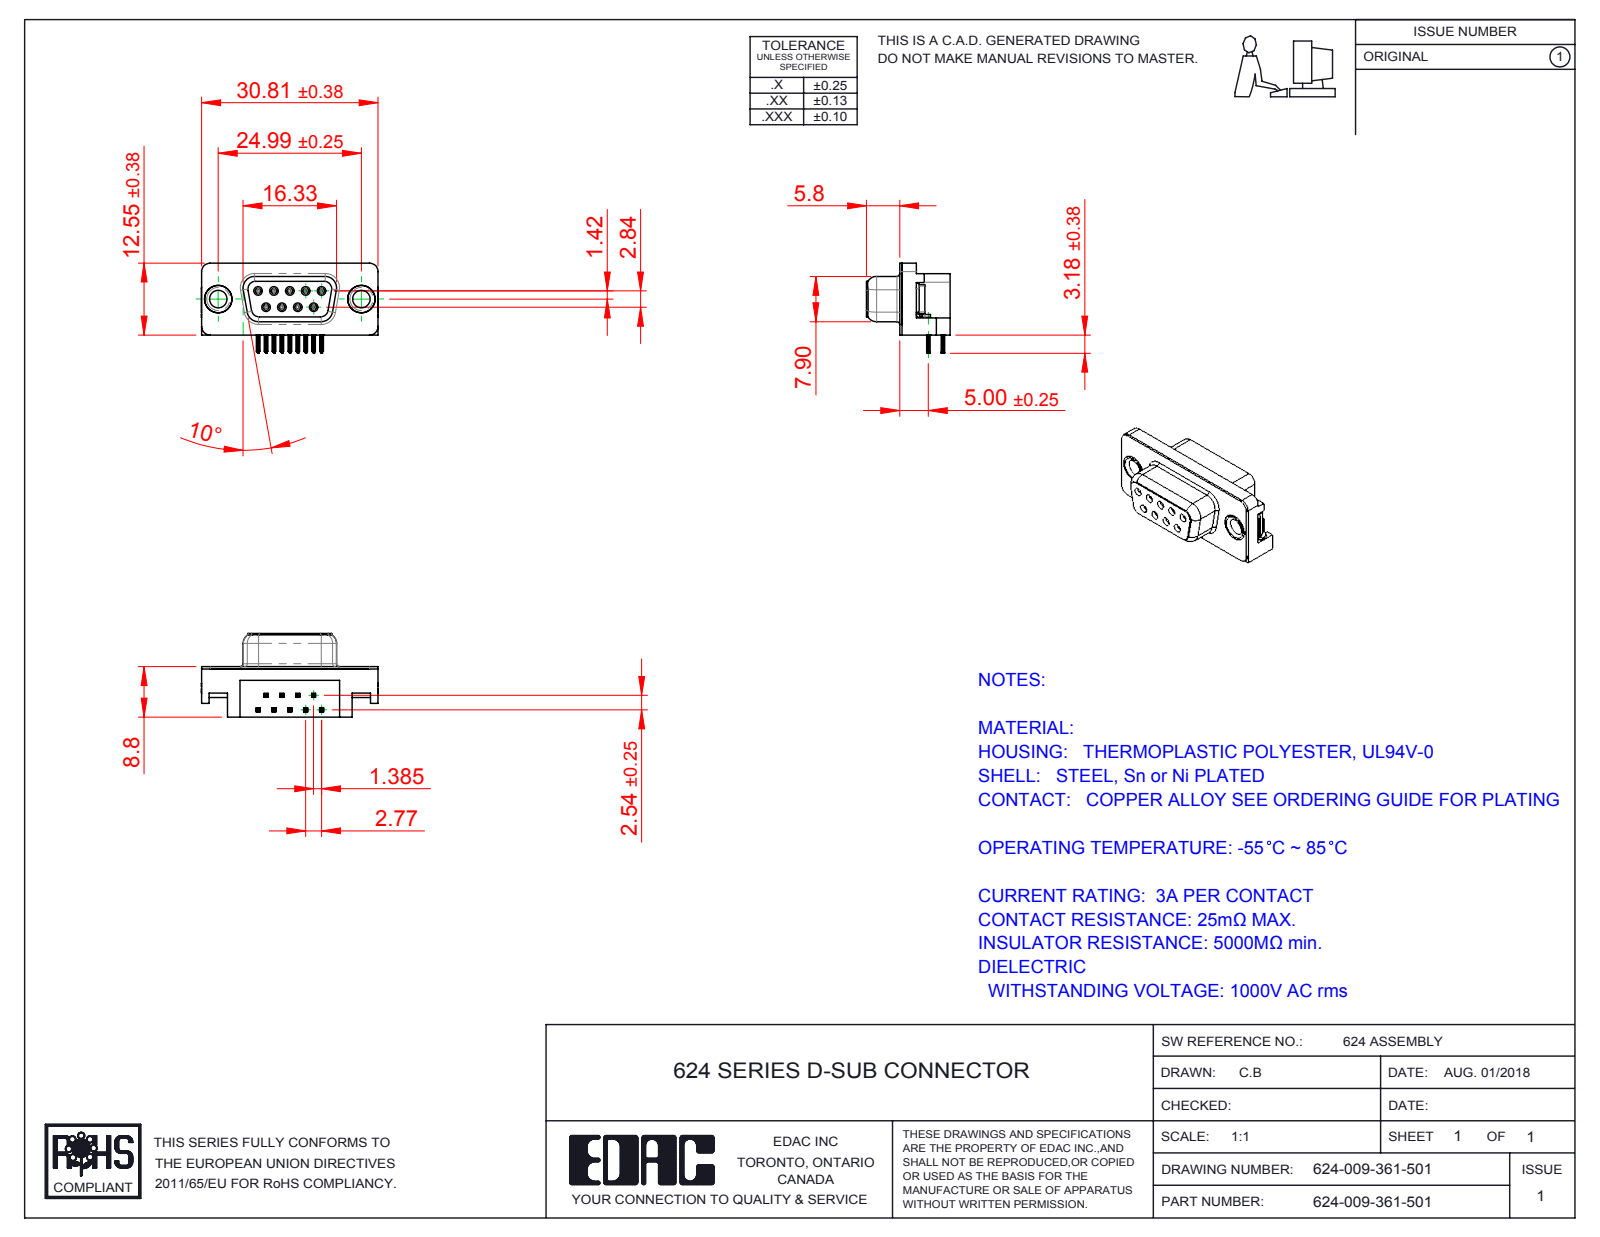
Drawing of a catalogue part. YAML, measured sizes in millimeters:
part_name: "624 Socket Bottom; 624 Shell_9 Socket; 624-009-361-501; 624 Non Board Mount (+3 more)"
step_written_by: "SolidWorks 2016 (CONFIG_CONTROL_DESIGN)"
units: millimeters
bodies: {solids: 15, faces: 1480, planar: 642, cylindrical: 388, other: 450}
overall_size: [30.89, 15.73, 14.6]
volume: 2925
surface_area: 4311
round_holes:
  - {diameter: 0.8, count: 9}
  - {diameter: 0.9, count: 9}
  - {diameter: 3.05, count: 2}
  - {diameter: 4, count: 2}
  - {diameter: 4.8, count: 2}
  - {diameter: 5, count: 2}
round_bosses_or_shafts:
  - {diameter: 1.2, count: 9}
  - {diameter: 4.9, count: 2}
  - {diameter: 4.75, count: 2}
  - {diameter: 3.85, count: 2}
partial_cylinders:
  - {radius: 0.1, count: 72}
  - {radius: 0.15, count: 36}
  - {radius: 0.35, count: 18}
  - {radius: 1, count: 18}
  - {radius: 0.34, count: 9}
  - {radius: 0.25, count: 8}
  - {radius: 1.35, count: 8}
  - {radius: 1.5, count: 7}
face_to_face_distances: [0.4, 8.4, 8.8, 2.9, 2.5, 6.2, 5.9, 0.35, 10.69, 10.34]
hole_center_spacings: [3.16, 2.77, 5.54, 5.03, 5.04, 8.31, 7.48, 7.49]
